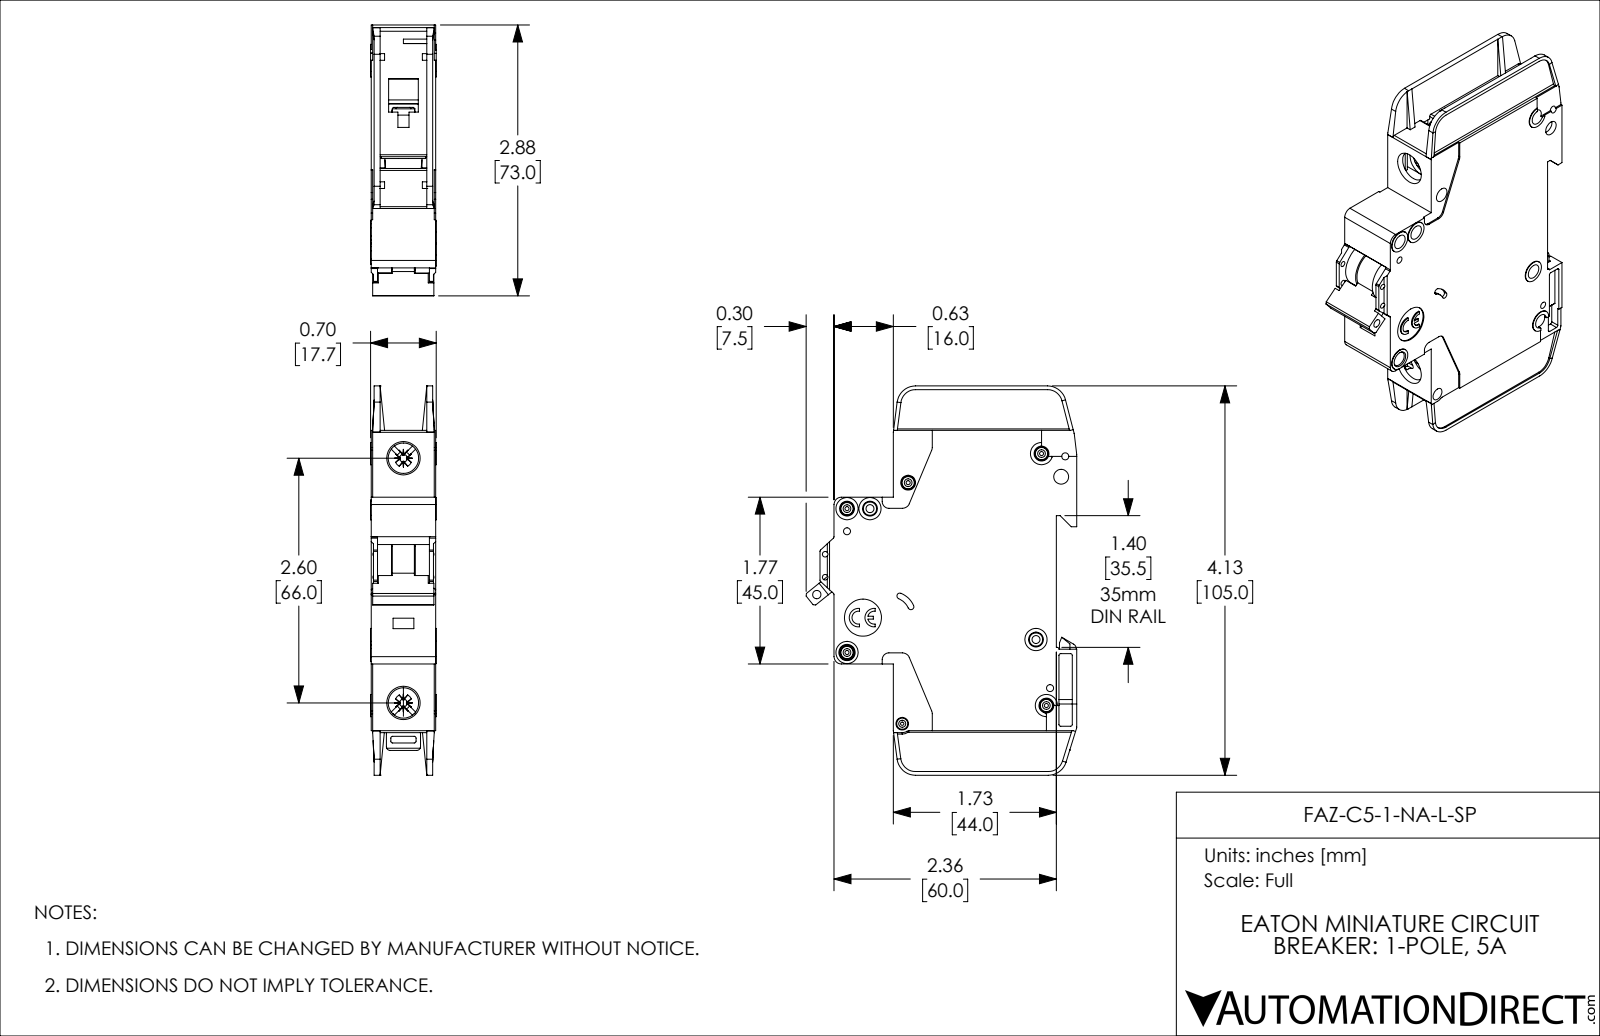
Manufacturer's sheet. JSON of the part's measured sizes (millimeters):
{"part_name": "FAZ-C5-1-NA-L-SP", "step_written_by": "SolidWorks 2019 (AUTOMOTIVE_DESIGN)", "units": "millimeters", "bodies": {"solids": 1, "faces": 1127, "planar": 671, "cylindrical": 357, "other": 99}, "overall_size": [105, 73.1, 17.7], "volume_mm3": 76720, "surface_area_mm2": 26460, "round_holes": [[4, 8], [1.1, 5], [1.9, 4], [1.5, 2], [2.2, 2], [8.2, 2], [0.9, 1], [2.3, 1], [2.5, 1], [3.4, 1], [10, 1]], "round_bosses_or_shafts": [[3.3, 5], [6, 4], [3, 2], [2.5, 1]], "partial_cylinders_radius": [[0.5, 42], [0.4, 10], [1, 10], [2, 8], [5, 5], [0.2, 4], [0.7, 4], [1.1, 4]], "face_to_face_distances": [1.2, 17.4, 15, 16.2, 2.4, 13.8, 0.4, 0.8, 12.6, 14.6], "hole_center_spacings": [6.2, 13.6, 22.1, 4.8, 5.1, 5.2, 5.6, 6.1]}
